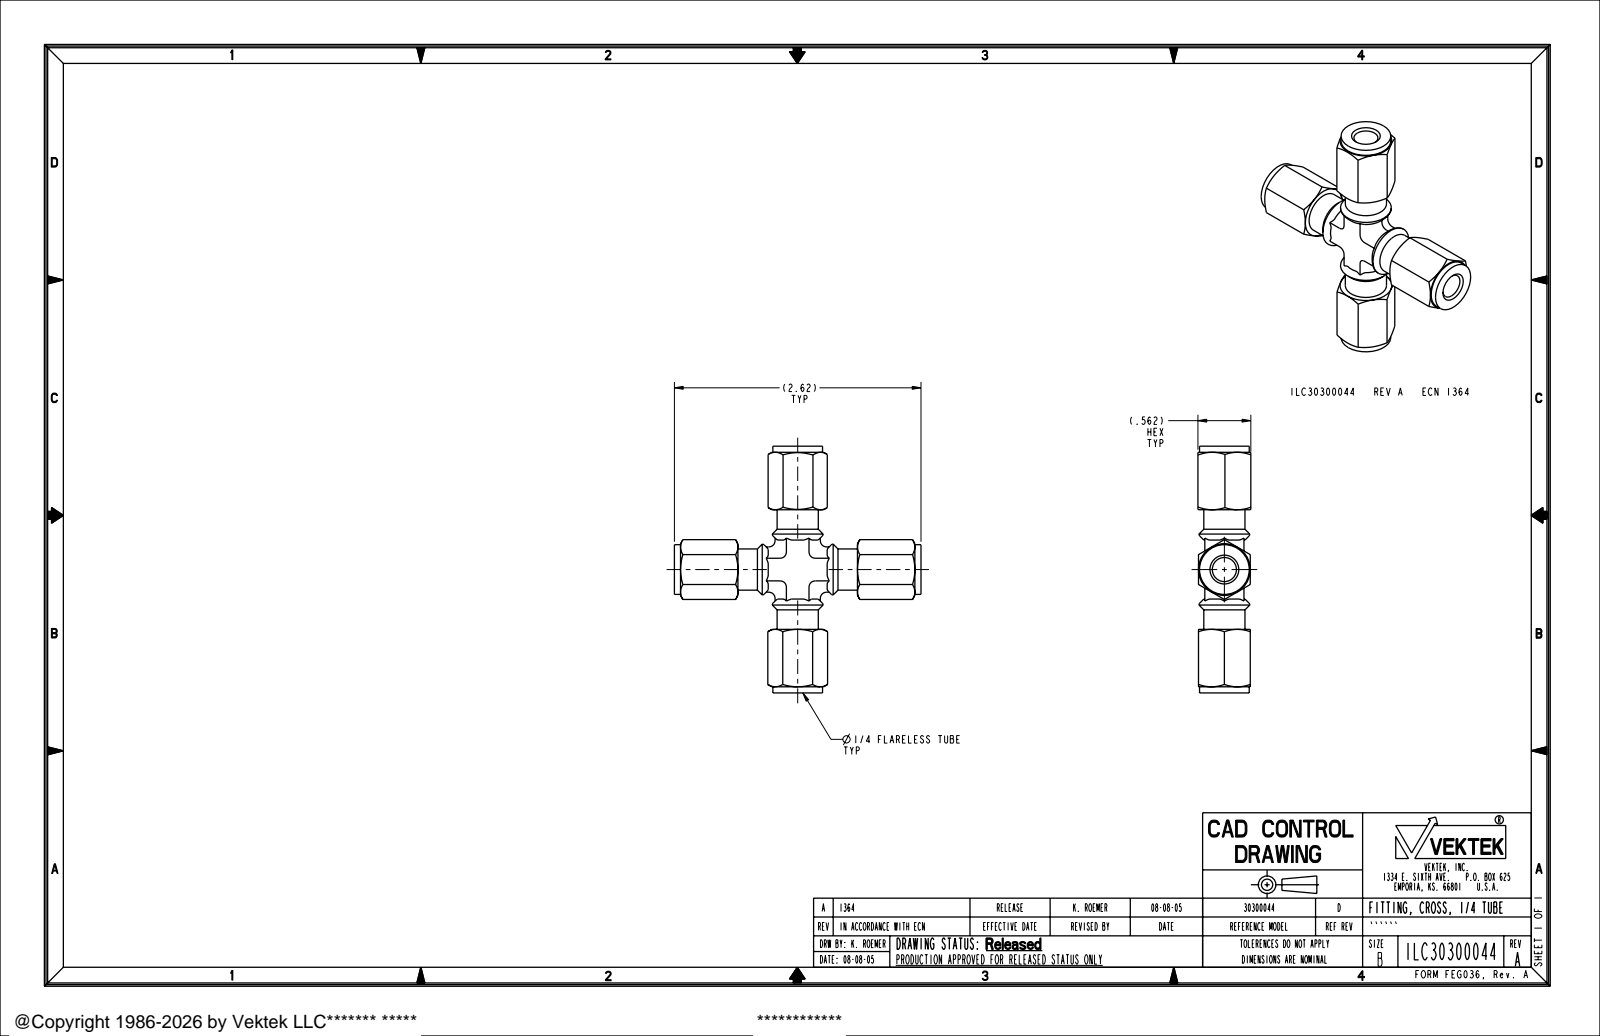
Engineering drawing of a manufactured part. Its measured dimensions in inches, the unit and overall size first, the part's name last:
Units: inches
Overall size (bounding box): 2.62 × 2.62 × 0.562
Round holes (diameter × count): ⌀0.256 ×2, ⌀0.437 ×2
Round bosses / shafts (diameter × count): ⌀0.528 ×2
Partial cylindrical surfaces — rounded edges, fillets, slot ends (radius × count): R0.08 ×8
Main face-to-face distances: 0.55, 0.55, 0.067, 0.483, 0.416, 0.067, 0.483, 0.073, 0.489, 0.556
Volume: 0.781 in³ · Surface area: 14.03 in²
Bodies: 1 solid, 210 faces (78 planar, 56 cylindrical, 76 other)
Part name (STEP PRODUCT): ILC30300044
STEP written by: PRO/ENGINEER BY PARAMETRIC TECHNOLOGY CORPORATION, 2004290 (AUTOMOTIVE_DESIGN_CC2)
